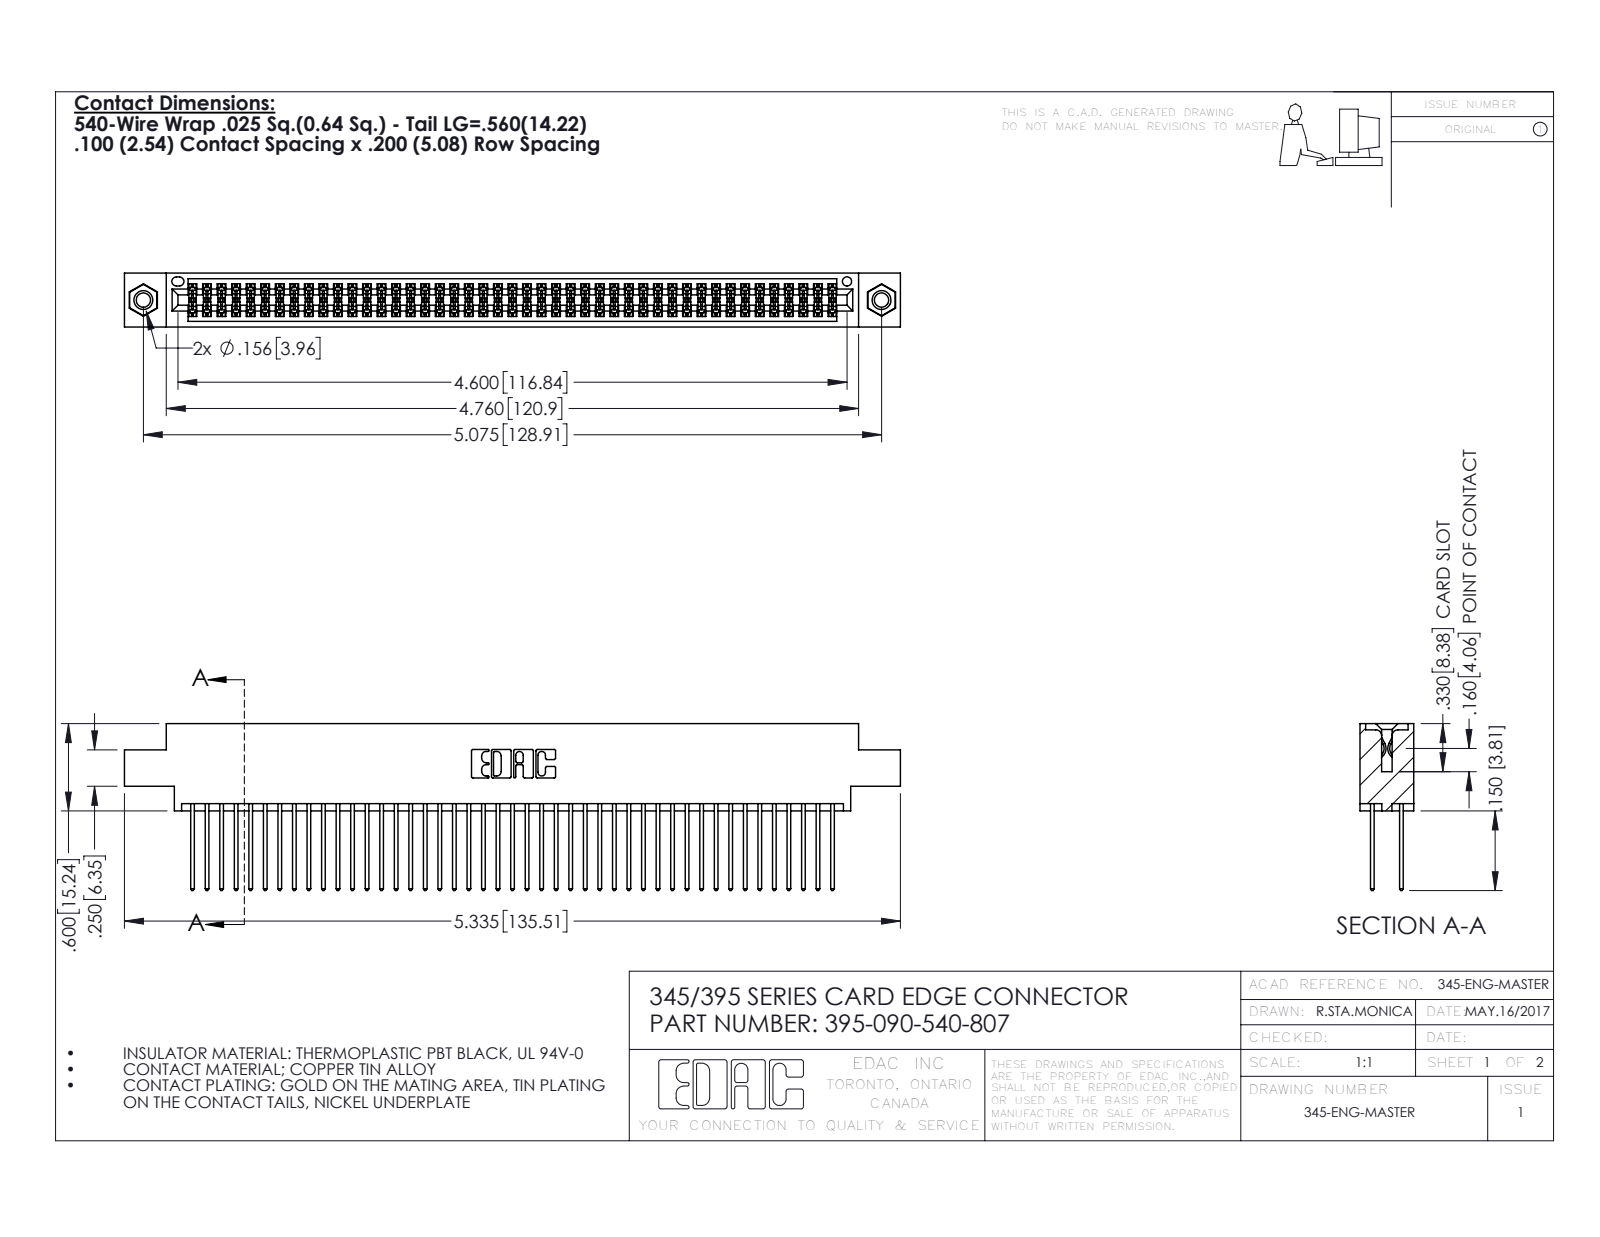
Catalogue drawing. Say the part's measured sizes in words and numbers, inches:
The part is named "345-250-001_345-250-005-103; 345 Part_0.170 Offset - 0.156 Dia-TI; 345-292-001_345-293-140; 395-090-540-807". Its 3-D file was written by "SolidWorks 2016 (CONFIG_CONTROL_DESIGN)". It is 93 solids with 4690 faces: 3086 planar, 1588 cylindrical and 16 other. Overall it measures 5.335 by 1.147 by 0.37 inches. Its volume is 0.818 cubic inches and its surface area 33.52 square inches. Round holes: 2 of diameter 0.098, 2 of diameter 0.125, 2 of diameter 0.156, 1 of diameter 0.064. Round bosses or shafts: 2 of diameter 0.155. Partial cylindrical surfaces (rounded edges, fillets, slot ends): 135 of radius 0.006, 90 of radius 0.01, 22 of radius 0.01, 6 of radius 0.007, 6 of radius 0.031, 3 of radius 0.026, 2 of radius 0.014, 2 of radius 0.019. The main face-to-face distances are 0.072, 0.298, 0.2, 0.098, 0.272, 0.025, 0.37, 0.225, 0.175, 0.149. The hole center spacings are 0.27, 4.839, 5.075.
